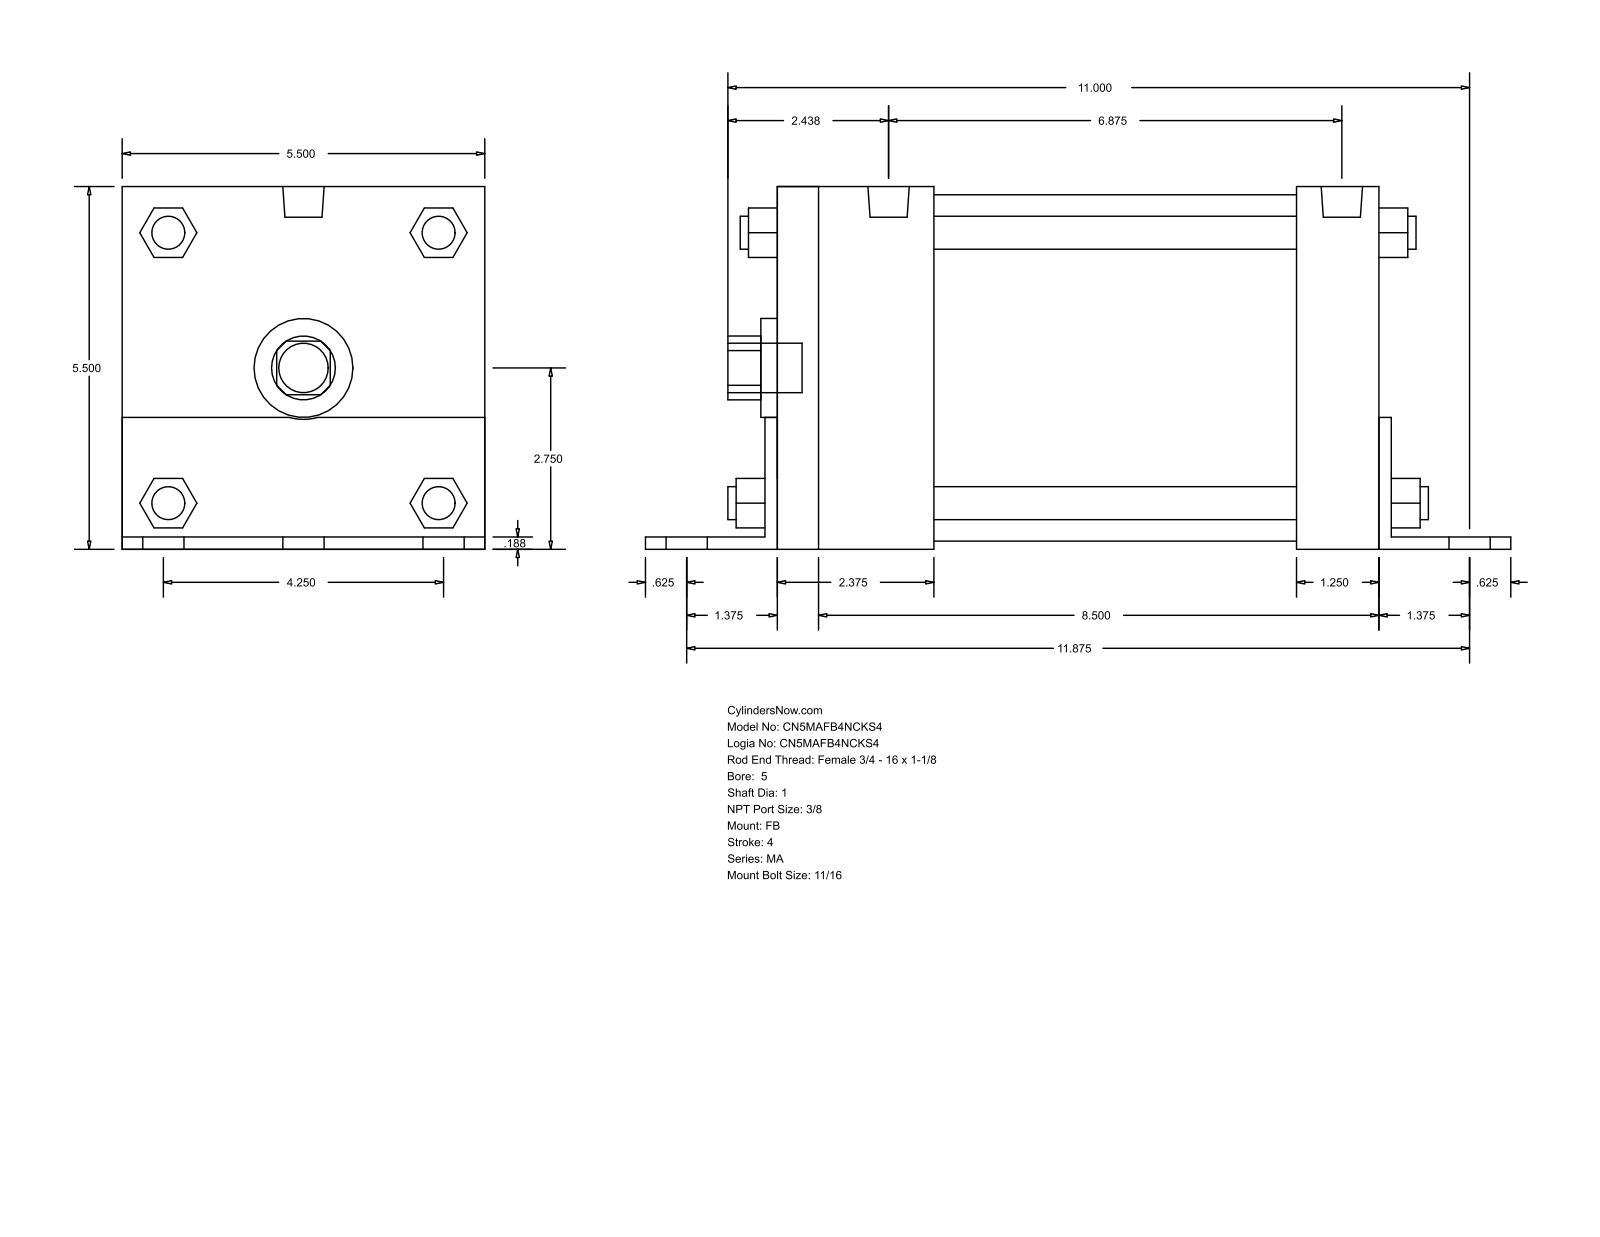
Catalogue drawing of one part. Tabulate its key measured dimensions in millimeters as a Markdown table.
| quantity | value |
| --- | --- |
| part name | MA_FB__0500_1 |
| STEP written by | GSSL Pune (CONFIG_CONTROL_DESIGN) |
| units | millimeters |
| bodies | 0 solids, 140 faces (105 planar, 35 cylindrical, 0 other) |
| overall size | 333.38 × 139.75 × 139.7 |
| round holes (diameter × count) | 25.4 × 1, 38.1 × 1, 133.35 × 1 |
| round bosses / shafts (diameter × count) | 17.46 × 6, 12.7 × 4, 11.11 × 4, 15.93 × 2, 19.05 × 1 |
| partial cylindrical surfaces (radius × count) | 12.29 × 1, 19.81 × 1 |
| main face-to-face distances | 139.7, 4.76, 139.75, 4.71, 134.99, 231.77, 4.77, 236.54, 236.53, 241.3 |
